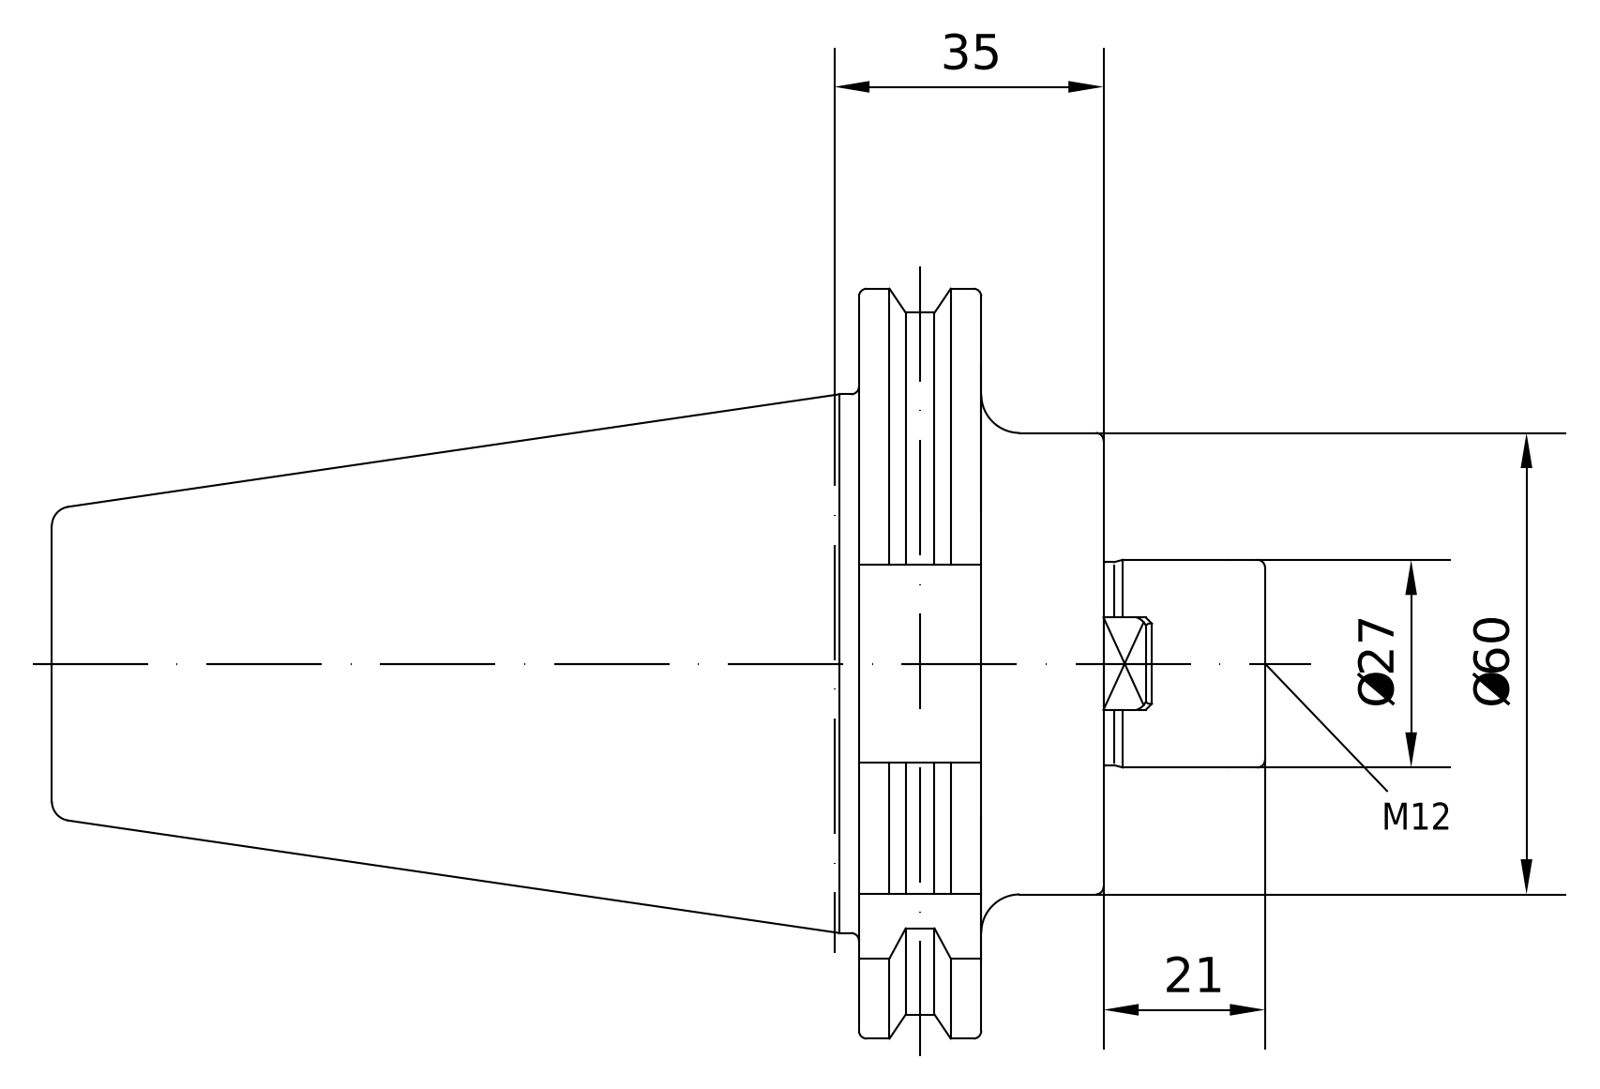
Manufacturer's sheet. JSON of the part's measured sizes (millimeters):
{"part_name": "50-350-27", "step_written_by": "PRO/ENGINEER BY PARAMETRIC TECHNOLOGY CORPORATION, 2010430 (CONFIG_CONTROL_DESIGN)", "units": "millimeters", "bodies": {"solids": 1, "faces": 110, "planar": 32, "cylindrical": 28, "other": 50}, "overall_size": [157.6, 97.47, 94], "volume_mm3": 396399, "surface_area_mm2": 49638, "round_holes": [[10.2, 1], [12, 1], [20.75, 1], [25.01, 1], [25.7, 1]], "round_bosses_or_shafts": [[91, 1], [69.15, 1], [60, 1], [27, 1], [24.01, 1]], "partial_cylinders_radius": [[1.75, 1], [48.74, 1]], "face_to_face_distances": [15.85, 31.8, 15.95, 52.8, 36.95, 21, 72.8, 104.8, 120.65, 136.6]}
